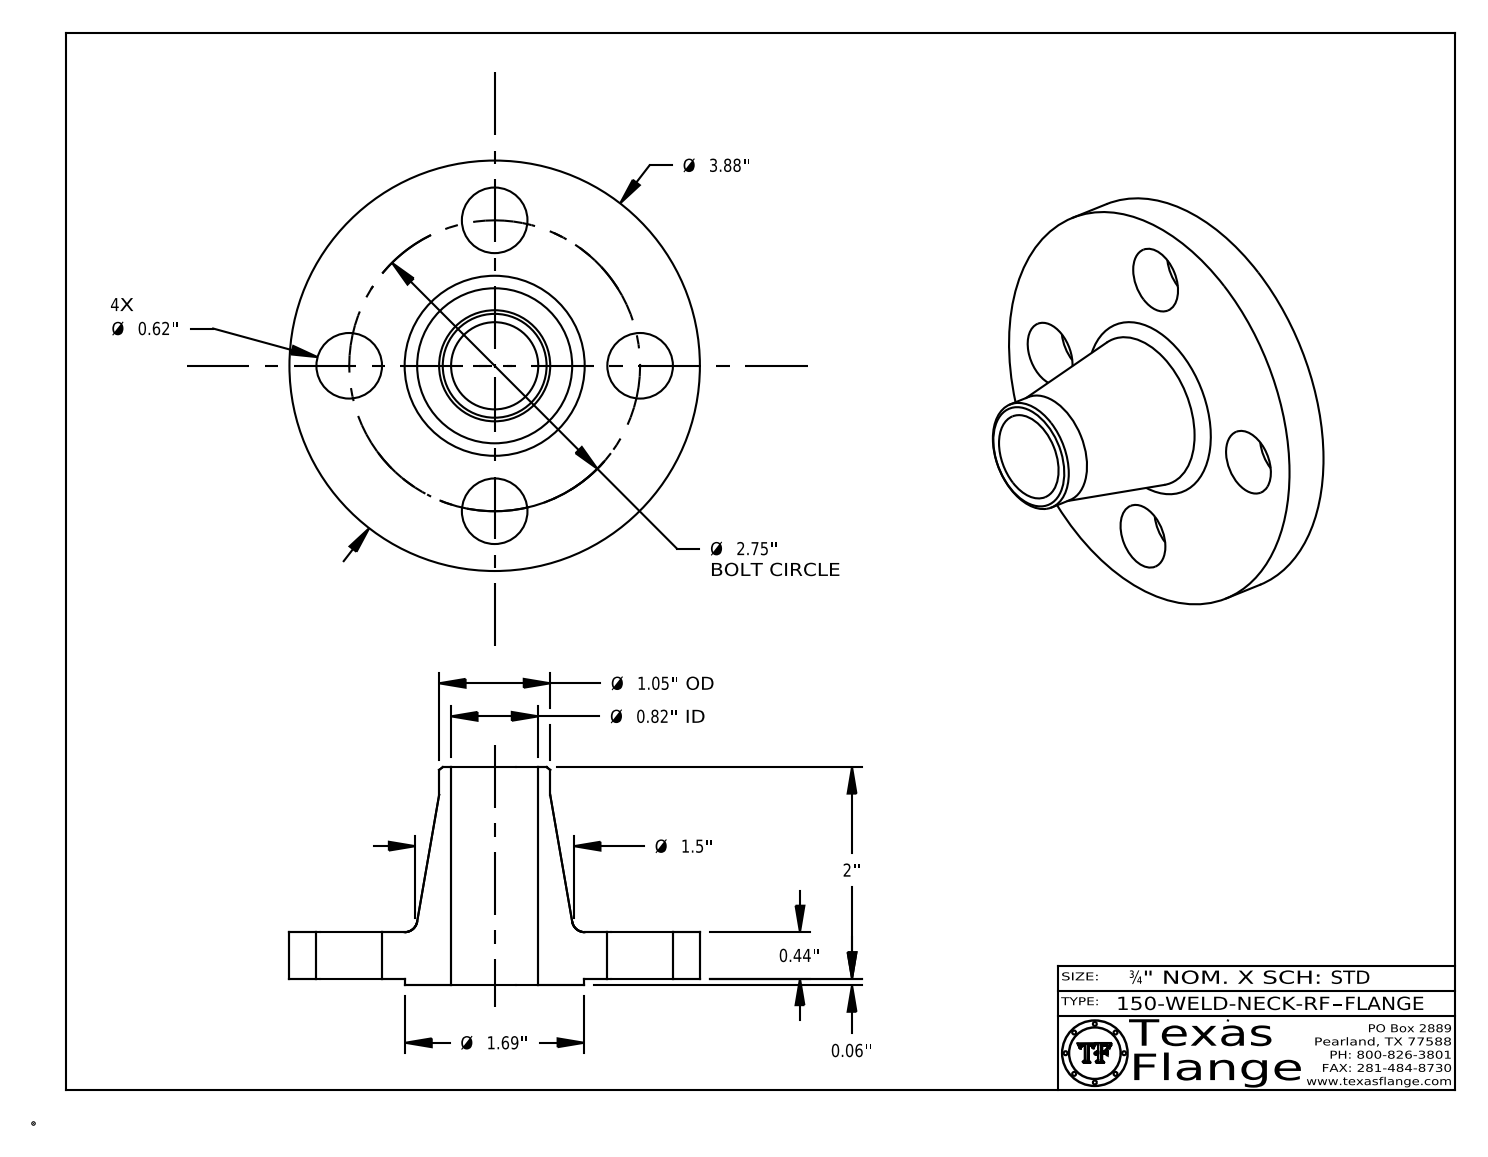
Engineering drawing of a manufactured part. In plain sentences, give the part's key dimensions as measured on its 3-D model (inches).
The part is named "150-WELD-NECK-RF". Its 3-D file was written by "CATIA V5 STEP AP214 (AUTOMOTIVE_DESIGN)". It is 1 solid with 411 faces: 369 planar, 36 cylindrical and 6 other. Overall it measures 3.88 by 3.88 by 2.063 inches. Its volume is 5.62 cubic inches and its surface area 39.75 square inches. Round holes: 4 of diameter 0.62, 1 of diameter 0.495, 1 of diameter 0.824. Round bosses or shafts: 8 of diameter 0.03, 1 of diameter 3.88, 1 of diameter 1.69, 1 of diameter 1.05, 1 of diameter 0.39. The main face-to-face distances are 0.44, 0.063, 0.503, 2.063, 2, 1.56, 0.488, 0.425, 0.015, 1.575. The hole center spacings are 1.375, 1.945, 1.052, 2.541, 2.75.
